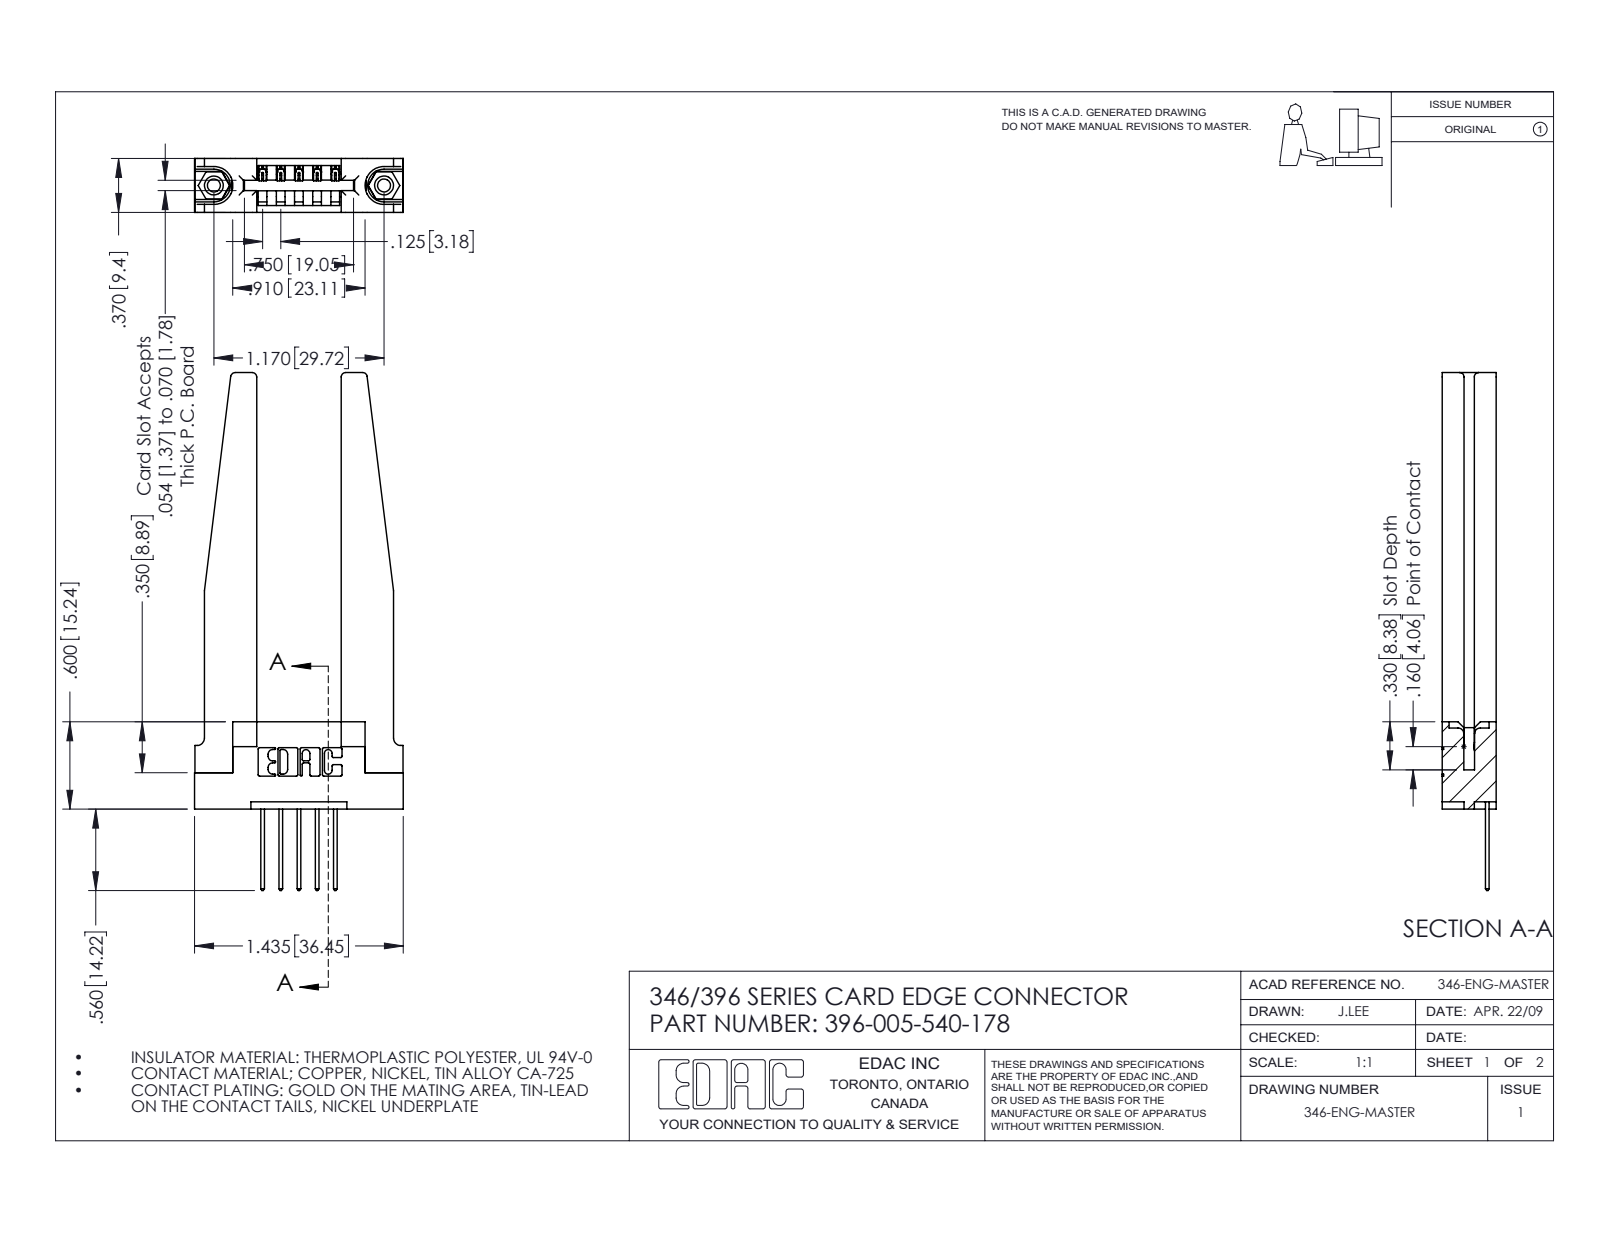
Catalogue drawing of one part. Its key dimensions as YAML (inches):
part_name: "346-220-078_345-220-078; 345-292-001_345-293-140; 345-250-001_345-250-001-102; 346 Part_Flush Mounting Lugs - 0.156 Dia-TH (+1 more)"
step_written_by: "SolidWorks 2016 (CONFIG_CONTROL_DESIGN)"
units: inches
bodies: {solids: 10, faces: 646, planar: 418, cylindrical: 176, other: 52}
overall_size: [3.56, 1.435, 0.37]
volume: 0.619
surface_area: 15.87
round_holes:
  - {diameter: 0.089, count: 2}
  - {diameter: 0.125, count: 2}
  - {diameter: 0.156, count: 2}
  - {diameter: 0.064, count: 1}
round_bosses_or_shafts:
  - {diameter: 0.155, count: 2}
partial_cylinders:
  - {radius: 0.01, count: 22}
  - {radius: 0.006, count: 10}
  - {radius: 0.01, count: 10}
  - {radius: 0.03, count: 8}
  - {radius: 0.007, count: 6}
  - {radius: 0.031, count: 6}
  - {radius: 0.026, count: 3}
  - {radius: 0.031, count: 2}
face_to_face_distances: [0.37, 0.15, 0.22, 0.25, 0.581, 0.148, 0.072, 0.102, 0.048, 0.322]
hole_center_spacings: [0.246, 0.969, 1.17]
